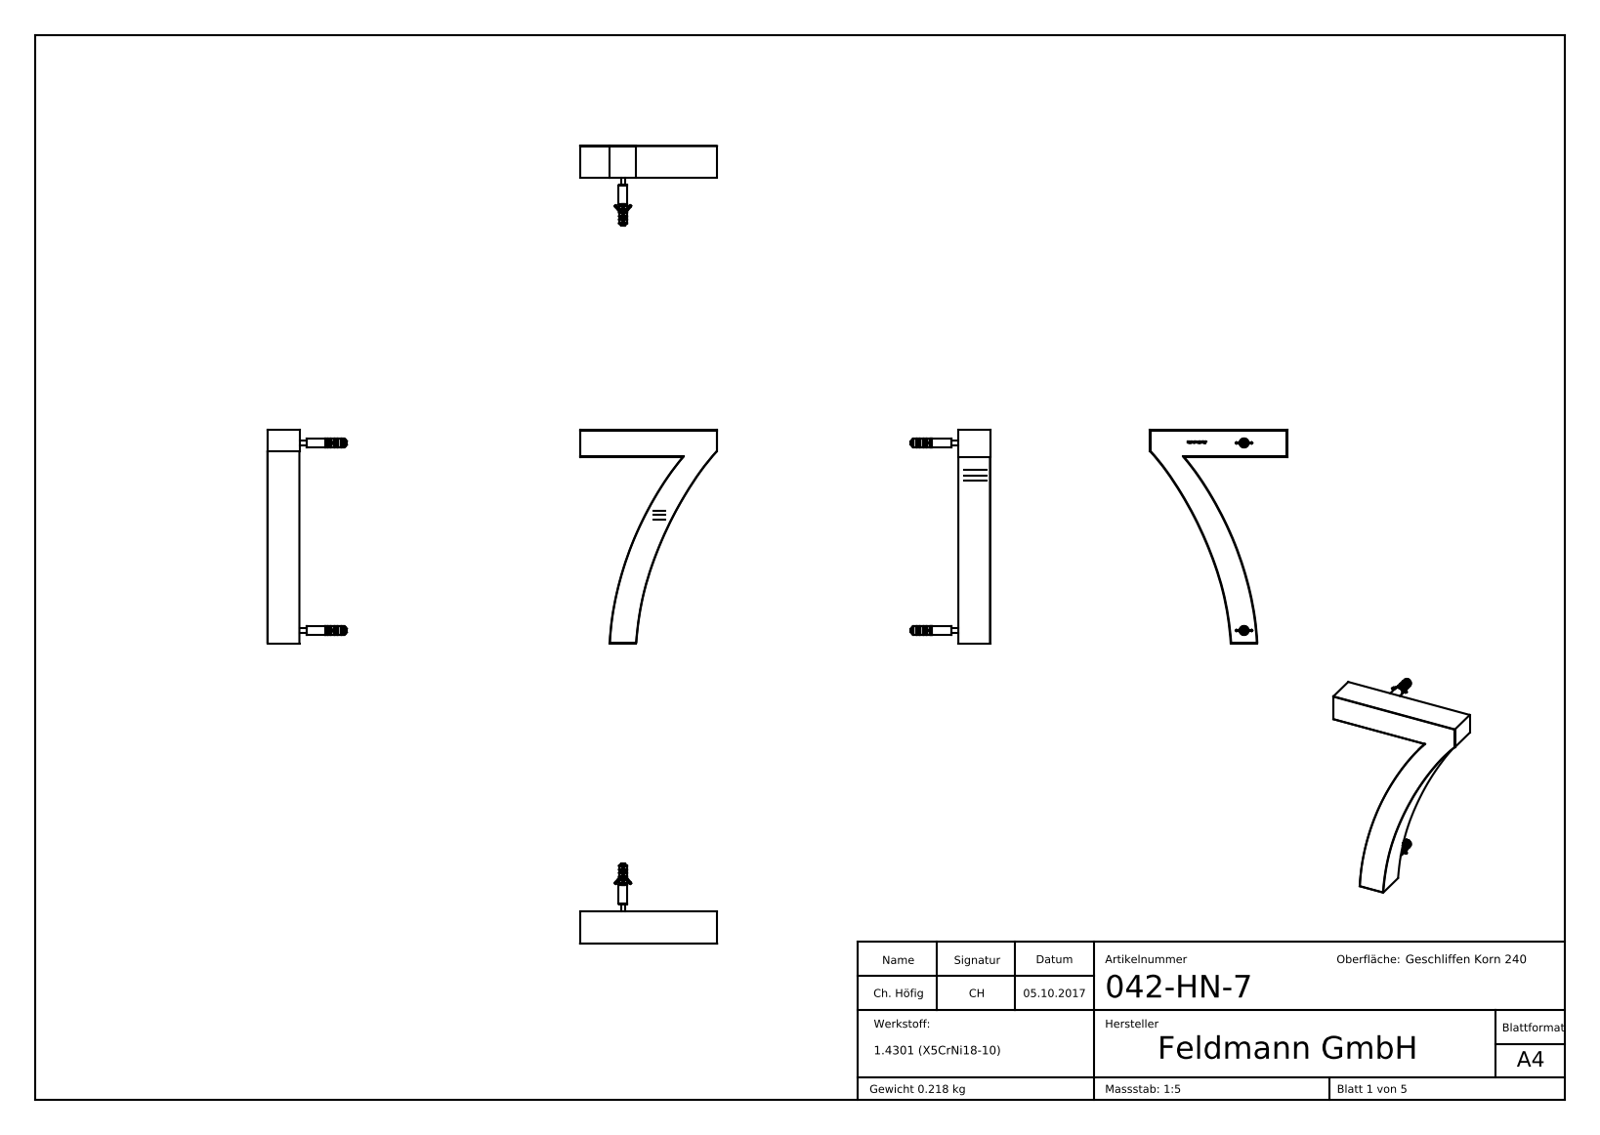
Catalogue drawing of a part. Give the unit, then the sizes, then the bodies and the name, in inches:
Units: inches
Overall size (bounding box): 7.874 × 6.013 × 5.077
Round holes (diameter × count): ⌀0.165 ×2
Round bosses / shafts (diameter × count): ⌀0.039 ×4, ⌀0.335 ×2, ⌀0.315 ×2, ⌀0.307 ×2, ⌀0.295 ×2, ⌀0.264 ×2, ⌀0.197 ×2, ⌀0.157 ×2
Partial cylindrical surfaces — rounded edges, fillets, slot ends (radius × count): R0.02 ×40, R0.008 ×34, R0.01 ×5
Main face-to-face distances: 0.02, 0.079, 0.965, 0.984, 0.945, 6.89, 7.854, 5.057, 6.909, 7.874
Hole centre spacings: 6.929
Volume: 1.833 in³ · Surface area: 93.38 in²
Bodies: 5 solids, 1117 faces (255 planar, 301 cylindrical, 561 other)
Part name (STEP PRODUCT): 042-HN-X Teil3_042-HN-X Teil3; 042-HN-X Teil2_042-HN-X Teil2; 042-HN-7; 042-HN-X Teil1_042-HN-7 Teil1
STEP written by: SolidWorks 2015 (CONFIG_CONTROL_DESIGN)
